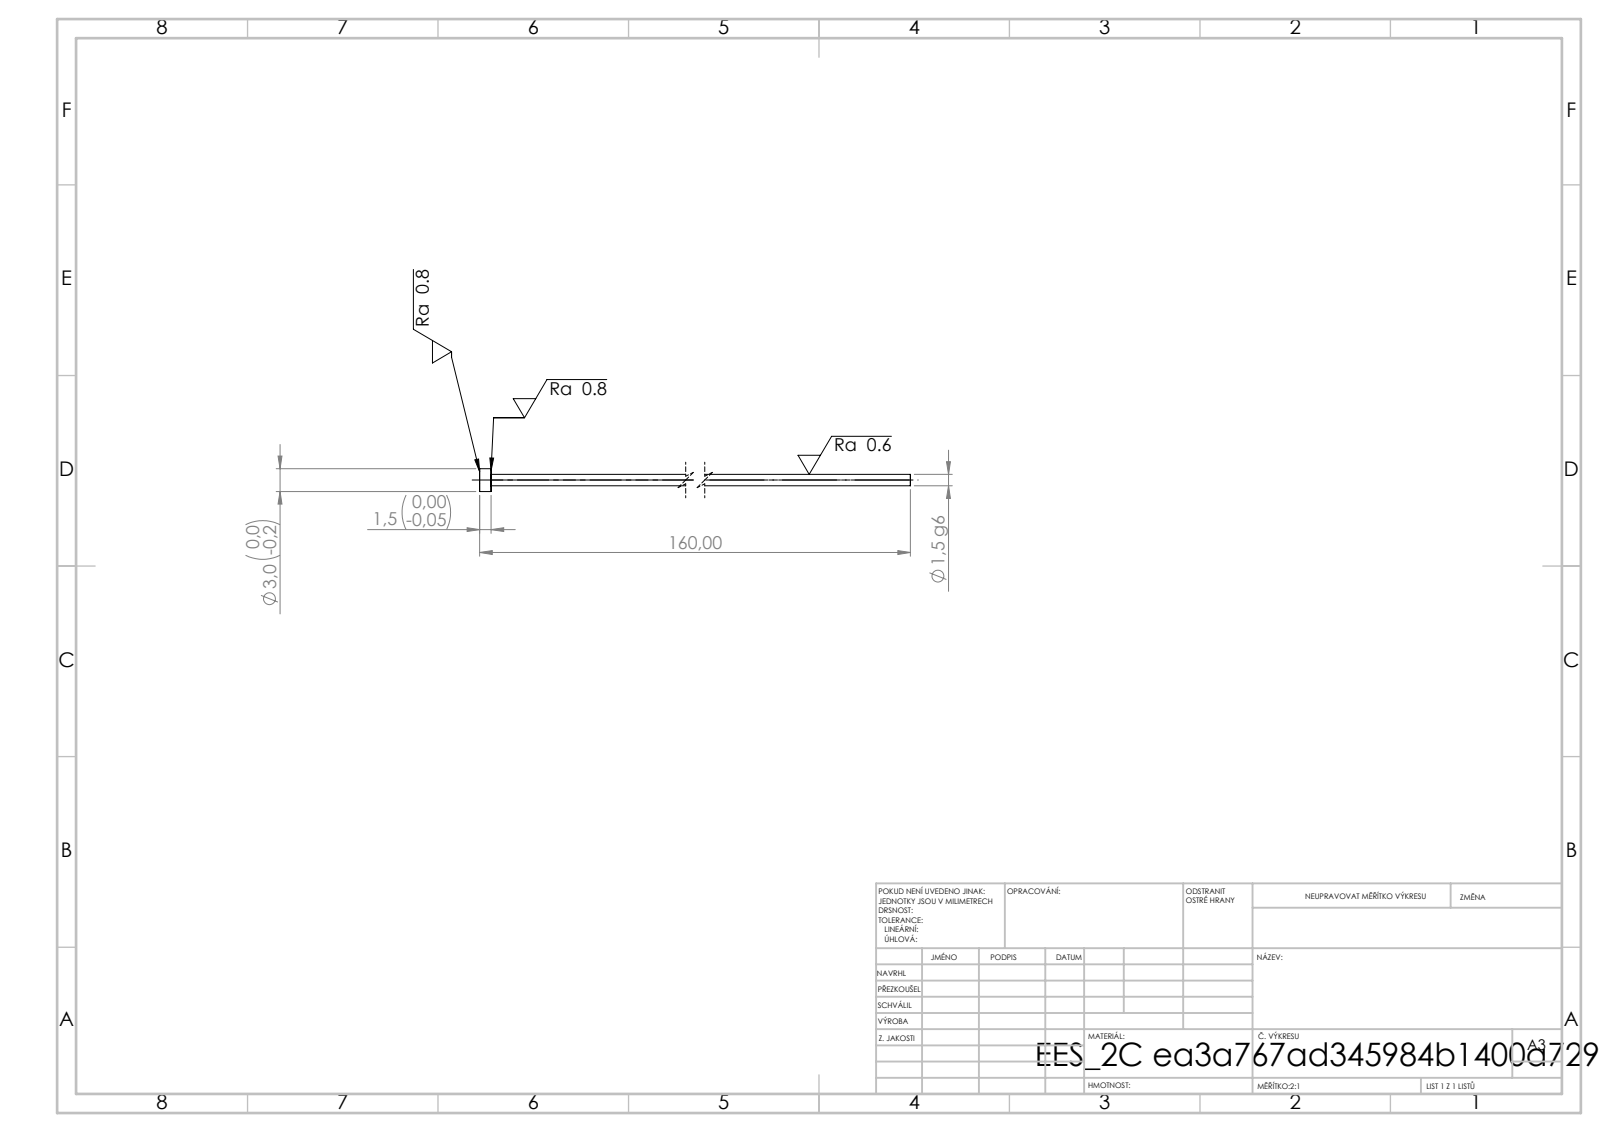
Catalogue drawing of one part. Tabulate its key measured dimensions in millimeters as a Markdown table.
| quantity | value |
| --- | --- |
| STEP written by | SolidWorks 2019 (CONFIG_CONTROL_DESIGN) |
| units | millimeters |
| bodies | 1 solid, 7 faces (3 planar, 4 cylindrical, 0 other) |
| overall size | 160 × 3 × 3 |
| volume | 291 mm³ |
| surface area | 775 mm² |
| round bosses / shafts (diameter × count) | 3 × 1, 1.5 × 1 |
| main face-to-face distances | 1.5, 160, 158.5 |
